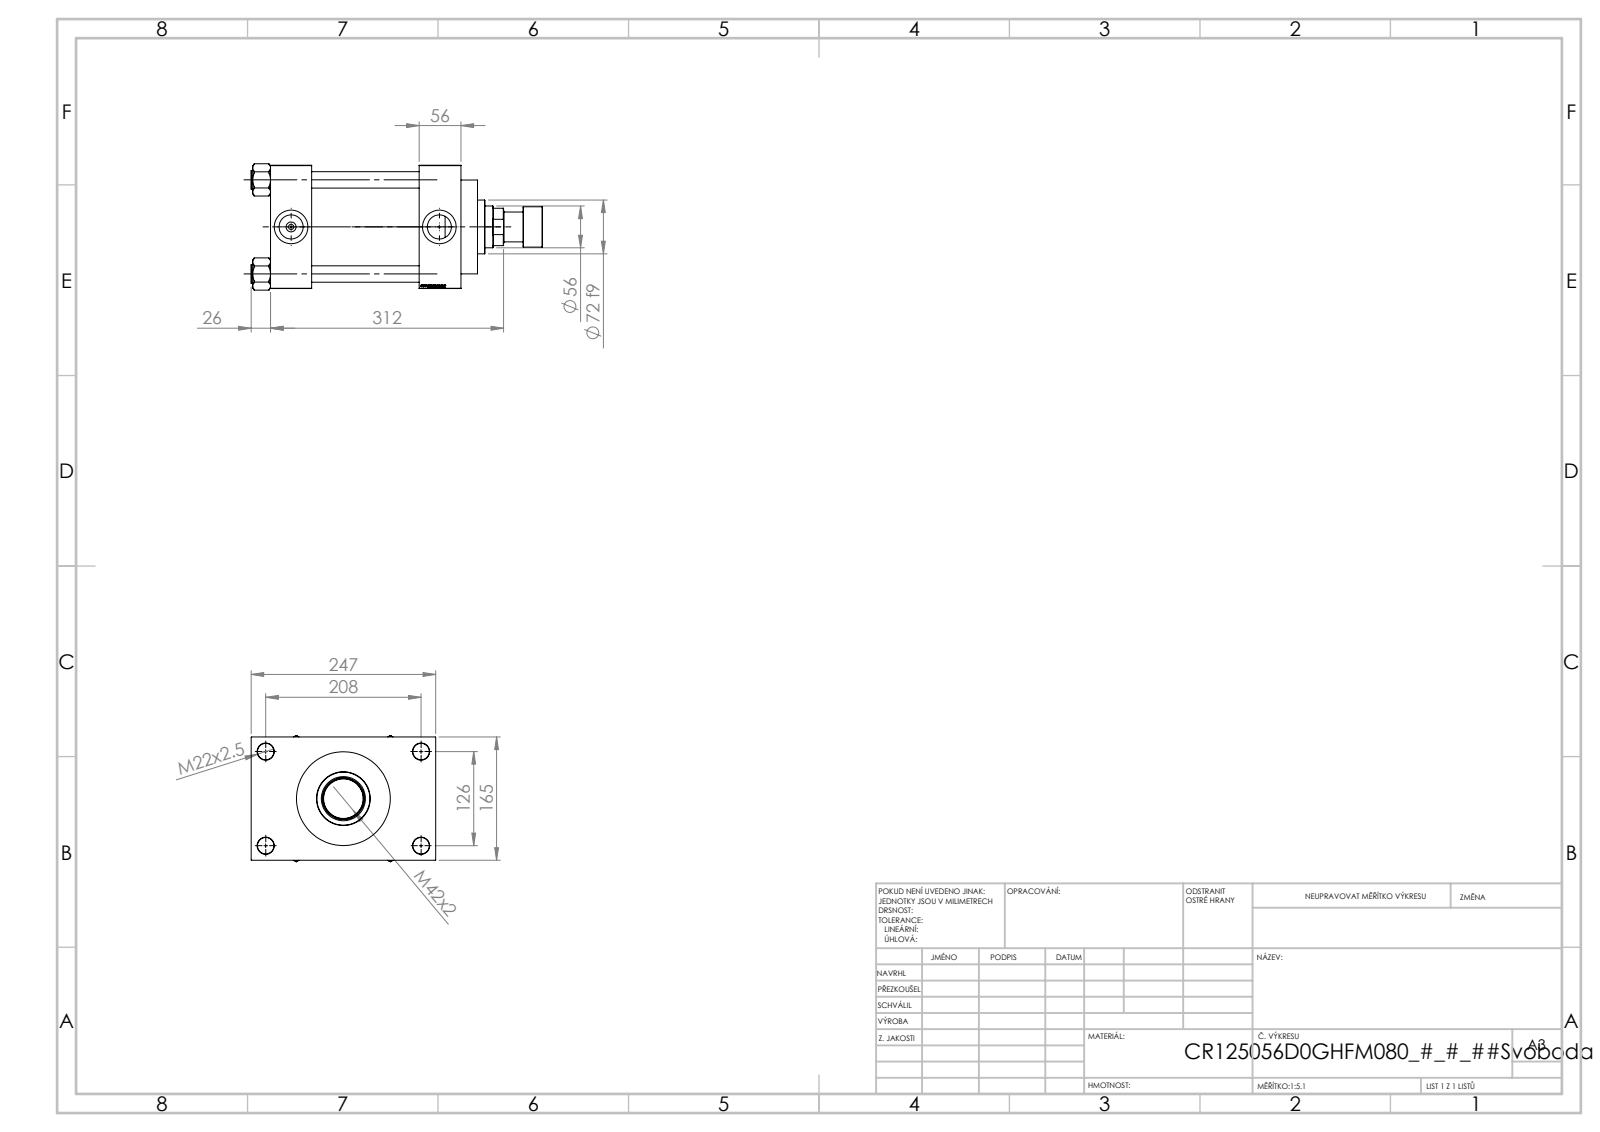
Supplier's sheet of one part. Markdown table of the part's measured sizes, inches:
| quantity | value |
| --- | --- |
| part name | NUT_M5_D; V215CR_D_Body; V215_VC_A; V215CR_VCP_D (+2 more) |
| STEP written by | SolidWorks 2019 (CONFIG_CONTROL_DESIGN) |
| units | inches |
| bodies | 12 solids, 1162 faces (548 planar, 90 cylindrical, 524 other) |
| overall size | 15.354 × 9.724 × 6.659 |
| volume | 325.1 in³ |
| surface area | 964.1 in² |
| round holes (diameter × count) | 0.866 × 8, 0.276 × 2, 1.269 × 2, 1.772 × 2, 1.594 × 1, 2.205 × 1, 2.323 × 1, 3.78 × 1, 4.921 × 1, 4.941 × 1 |
| round bosses / shafts (diameter × count) | 0.984 × 4, 5.157 × 1, 2.835 × 1, 2.126 × 1, 1.575 × 1 |
| main face-to-face distances | 6.496, 5.669, 2.165, 7.835, 2.205, 10.039, 7.874, 1.614, 8.11, 9.202 |
| hole center spacings | 1.616, 3.505, 4.787, 4.957, 5.215, 6.573, 8.233, 4.961 |
